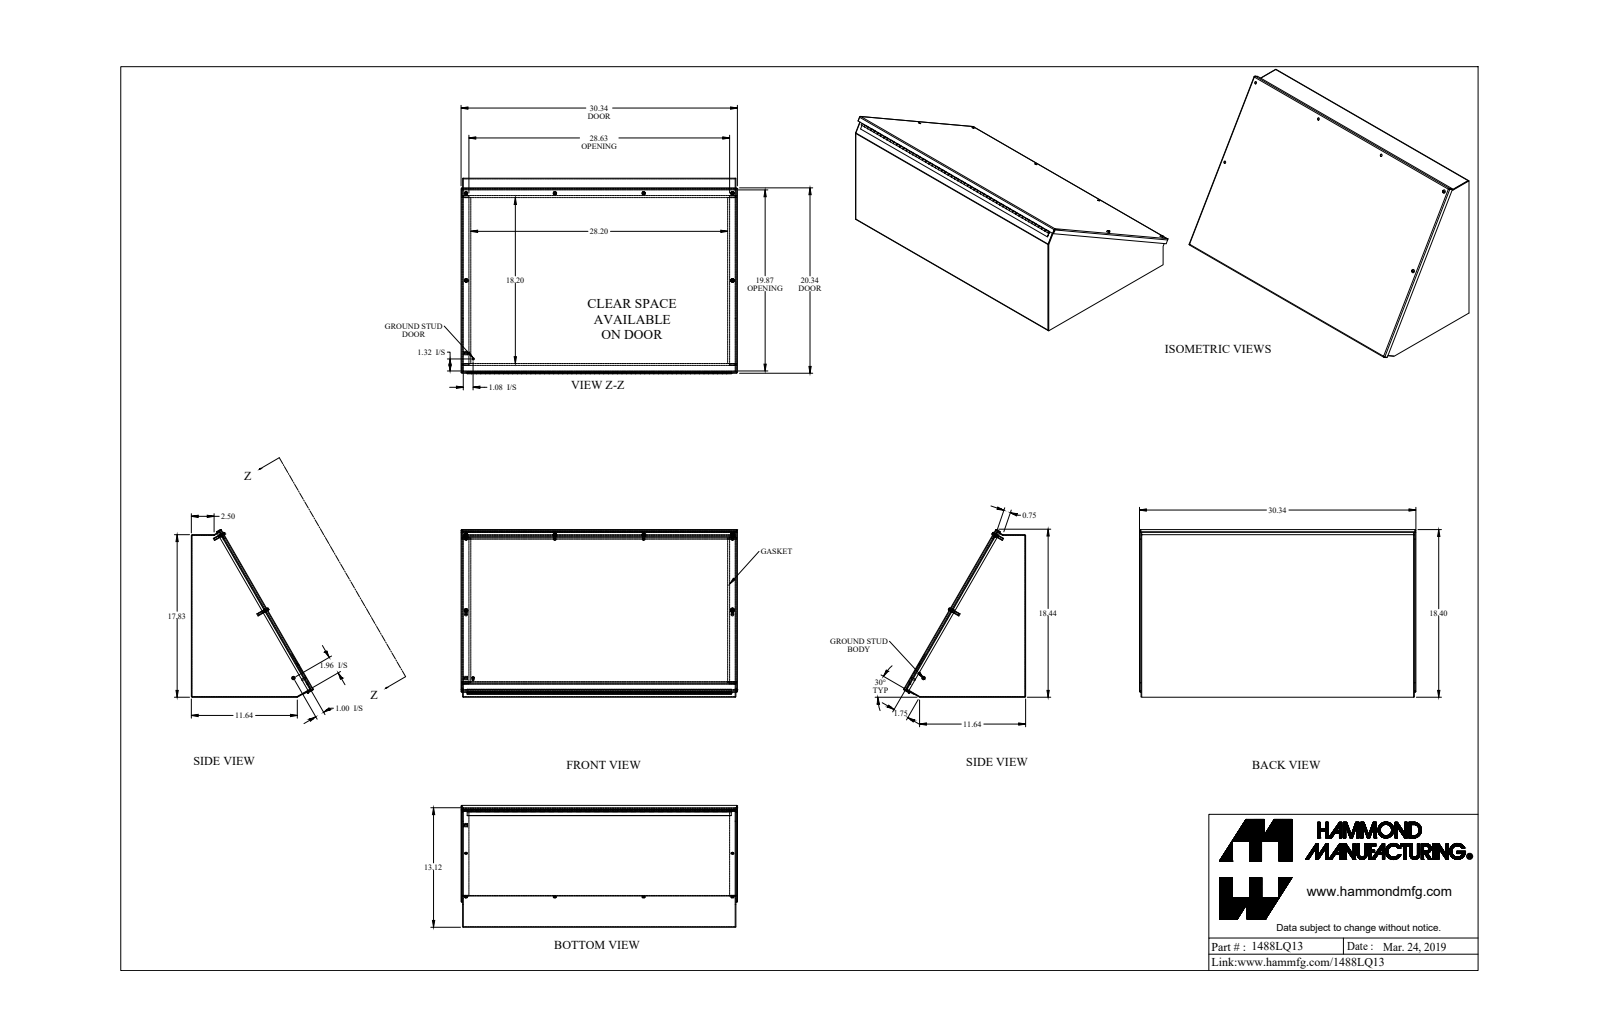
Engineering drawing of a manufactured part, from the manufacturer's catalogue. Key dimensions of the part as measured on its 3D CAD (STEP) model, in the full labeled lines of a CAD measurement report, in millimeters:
Part name (STEP PRODUCT): 1488LQ13_Default
STEP written by: SolidWorks 2019 (CONFIG_CONTROL_DESIGN)
Units: millimetres
Bodies: 21 solids, 918 faces (599 planar, 279 cylindrical, 40 other)
Overall size (bounding box): 770.7 × 467.3 × 339.7
Volume: 2 843 000 mm³ · Surface area: 2 872 000 mm²
Round holes (diameter × count): ⌀4 ×6, ⌀6.4 ×6, ⌀4 ×1
Round bosses / shafts (diameter × count): ⌀9.9 ×6, ⌀7 ×4, ⌀7 ×2, ⌀4.8 ×2, ⌀3.8 ×2, ⌀9.5 ×1, ⌀6.4 ×1, ⌀4.8 ×1
Partial cylindrical surfaces — rounded edges, fillets, slot ends (radius × count): R0.9 ×12, R2.7 ×12, R4.1 ×6, R3.2 ×2, R4.3 ×2
Main face-to-face distances: 1.8, 760.2, 758.3, 762, 451.1, 6.4, 5, 3.2, 3.2, 452.9
Hole centre spacings: 247.7, 495.3, 247.7, 551.7, 743, 743, 0.4, 242.9
